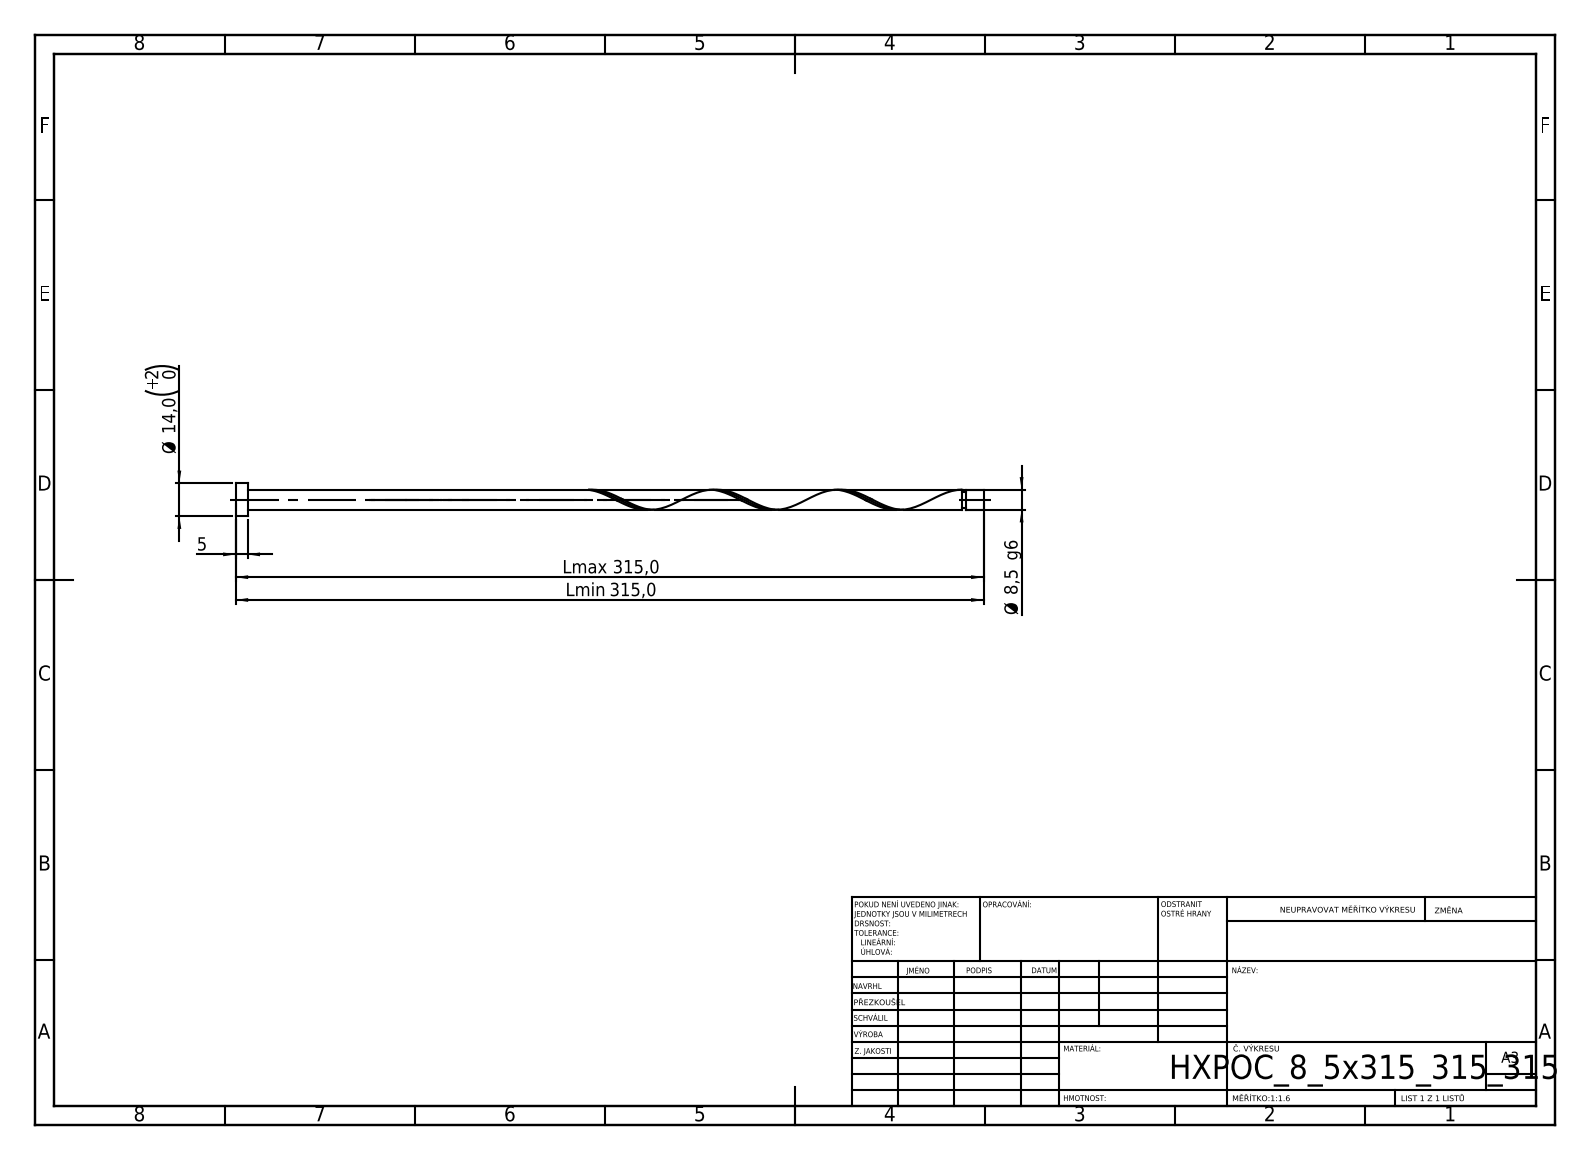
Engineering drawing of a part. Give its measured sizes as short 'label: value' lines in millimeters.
written by: SolidWorks 2019 (CONFIG_CONTROL_DESIGN)
unit: mm
bodies: 1 solid, 21 faces (6 planar, 14 cylindrical, 1 other)
size: 315 × 14 × 14
volume: 18 155 mm³; area: 8 986 mm²
bosses: 1× ⌀14, 1× ⌀8.5, 1× ⌀6.8
face distances: 5, 315, 310, 307.69, 302.69, 7.31, 305.99, 300.99, 1.7, 9.01
